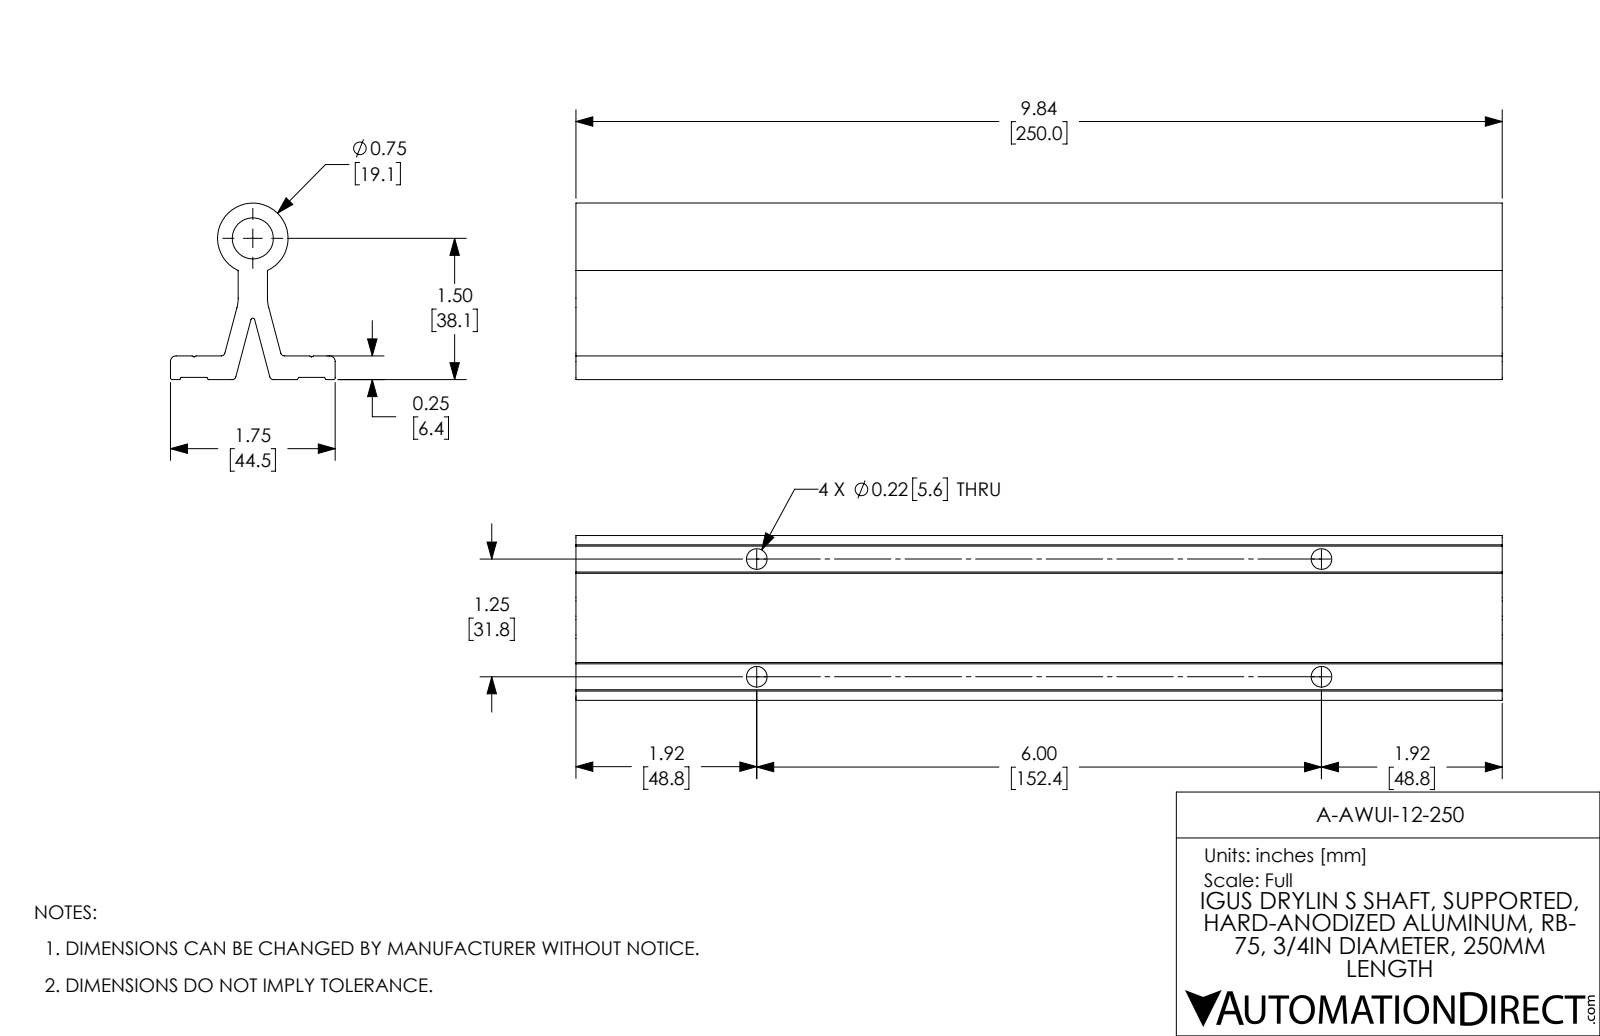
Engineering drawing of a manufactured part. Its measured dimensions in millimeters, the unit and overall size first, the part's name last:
Units: millimetres
Overall size (bounding box): 250 × 47.6 × 44.5
Round holes (diameter × count): ⌀5.6 ×4, ⌀11.1 ×1
Round bosses / shafts (diameter × count): ⌀19.1 ×1
Partial cylindrical surfaces — rounded edges, fillets, slot ends (radius × count): R1 ×4, R0.5 ×3, R1.5 ×2, R10 ×2
Main face-to-face distances: 4.5, 6.4, 0.6, 5.8, 7.9, 18.3, 26.2, 44.5, 26.2, 18.3
Hole centre spacings: 31.8, 152.4, 155.7
Volume: 151 600 mm³ · Surface area: 62 460 mm²
Bodies: 1 solid, 58 faces (36 planar, 22 cylindrical, 0 other)
Part name (STEP PRODUCT): A-AWUI-12-250
STEP written by: SolidWorks 2017 (AUTOMOTIVE_DESIGN)
